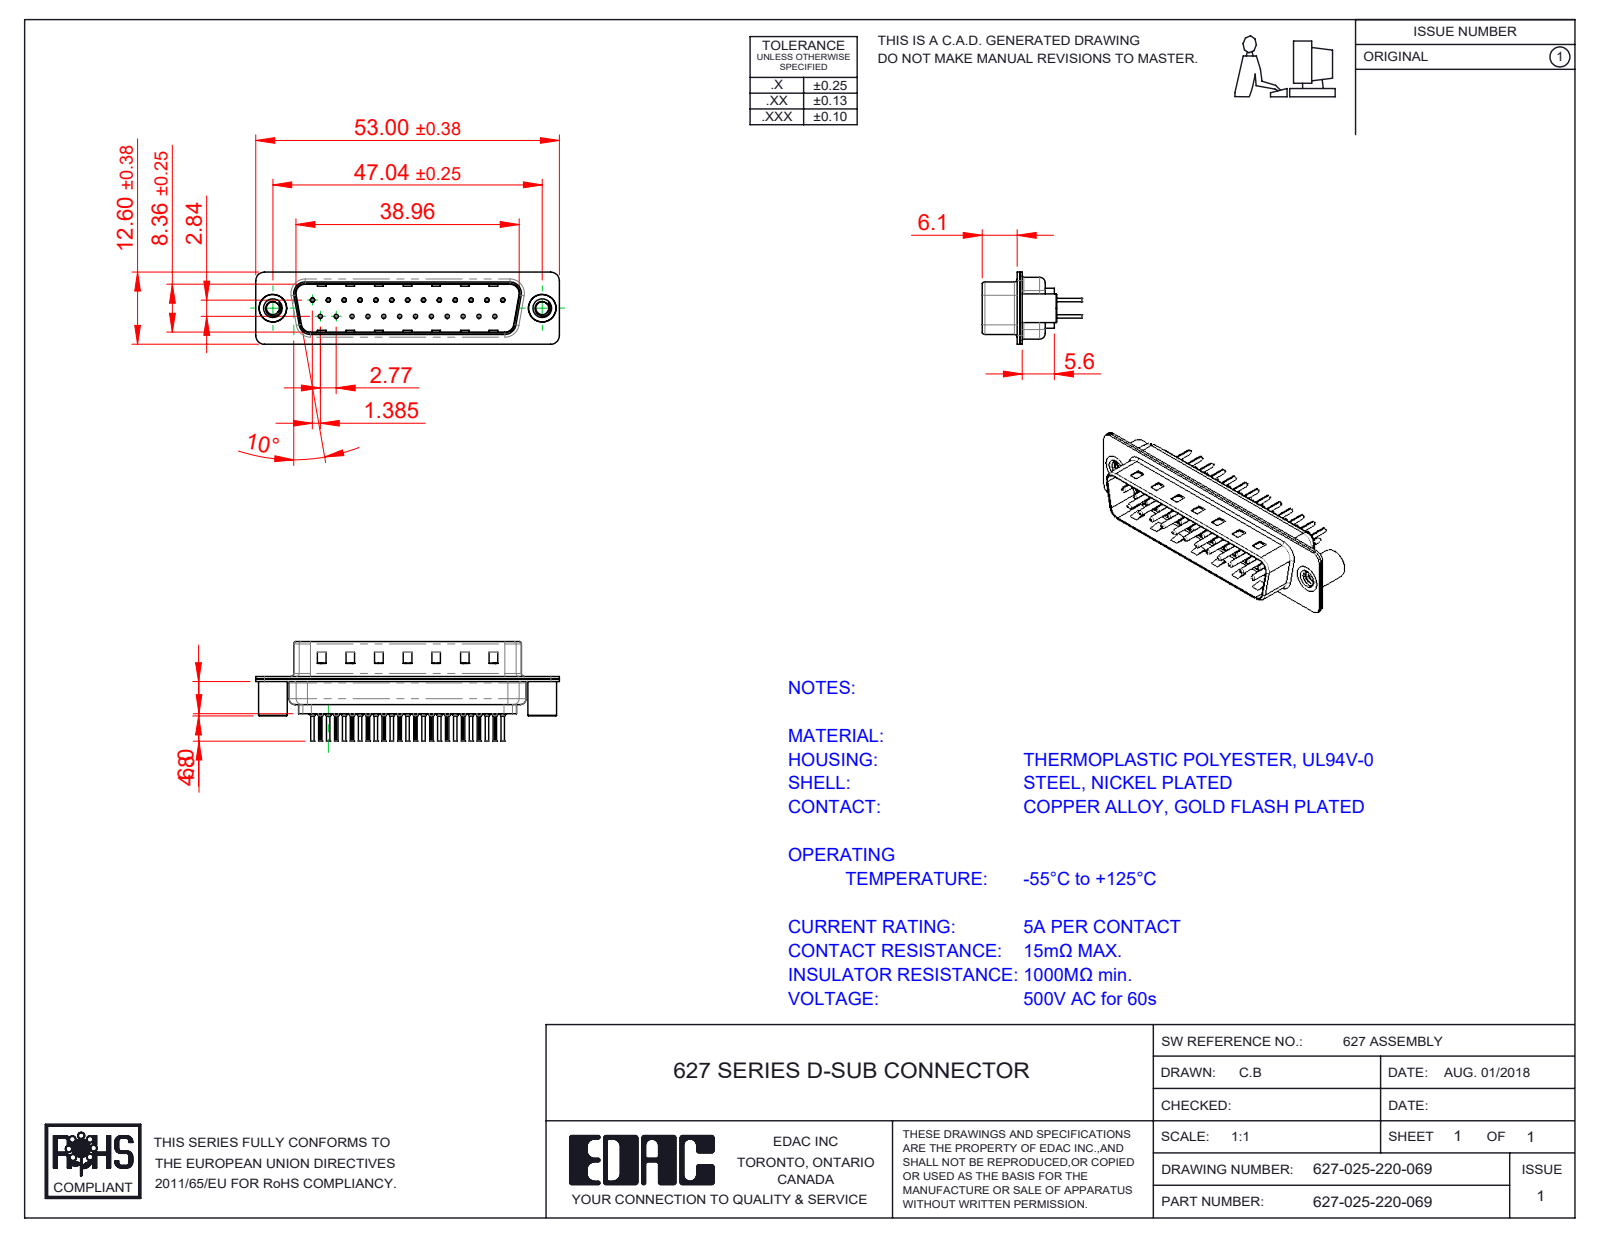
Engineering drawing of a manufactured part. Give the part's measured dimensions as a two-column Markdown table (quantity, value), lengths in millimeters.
| quantity | value |
| --- | --- |
| part name | 627 Contact Row 1_20L; 627 4-40 Threaded Standoff BS; 627 Housing_25 LP; 627 Shell Front_25 Contacts (+3 more) |
| STEP written by | SolidWorks 2020 (CONFIG_CONTROL_DESIGN) |
| units | millimeters |
| bodies | 30 solids, 2848 faces (771 planar, 1082 cylindrical, 995 other) |
| overall size | 53 × 17.3 × 12.6 |
| volume | 2 779 mm³ |
| surface area | 7 995 mm² |
| round holes (diameter × count) | 0.2 × 25, 0.35 × 25, 1.1 × 25, 1.6 × 25, 2.26 × 2, 4 × 2, 4.8 × 2 |
| round bosses / shafts (diameter × count) | 2 × 25, 1.5 × 25, 0.75 × 25, 0.6 × 25, 5 × 2, 4.9 × 2 |
| partial cylindrical surfaces (radius × count) | 0.1 × 50, 1.5 × 16, 2 × 12, 0.5 × 8, 1.6 × 8, 0.25 × 4, 0.6 × 4, 0.65 × 4 |
| main face-to-face distances | 0.4, 0.45, 0.82, 9.58, 8.76, 0.9, 1.5, 6.5, 1.4, 6.05 |
| hole center spacings | 3.16, 8.31, 2.77, 5.54, 11.08, 16.62, 5.03, 5.04 |
